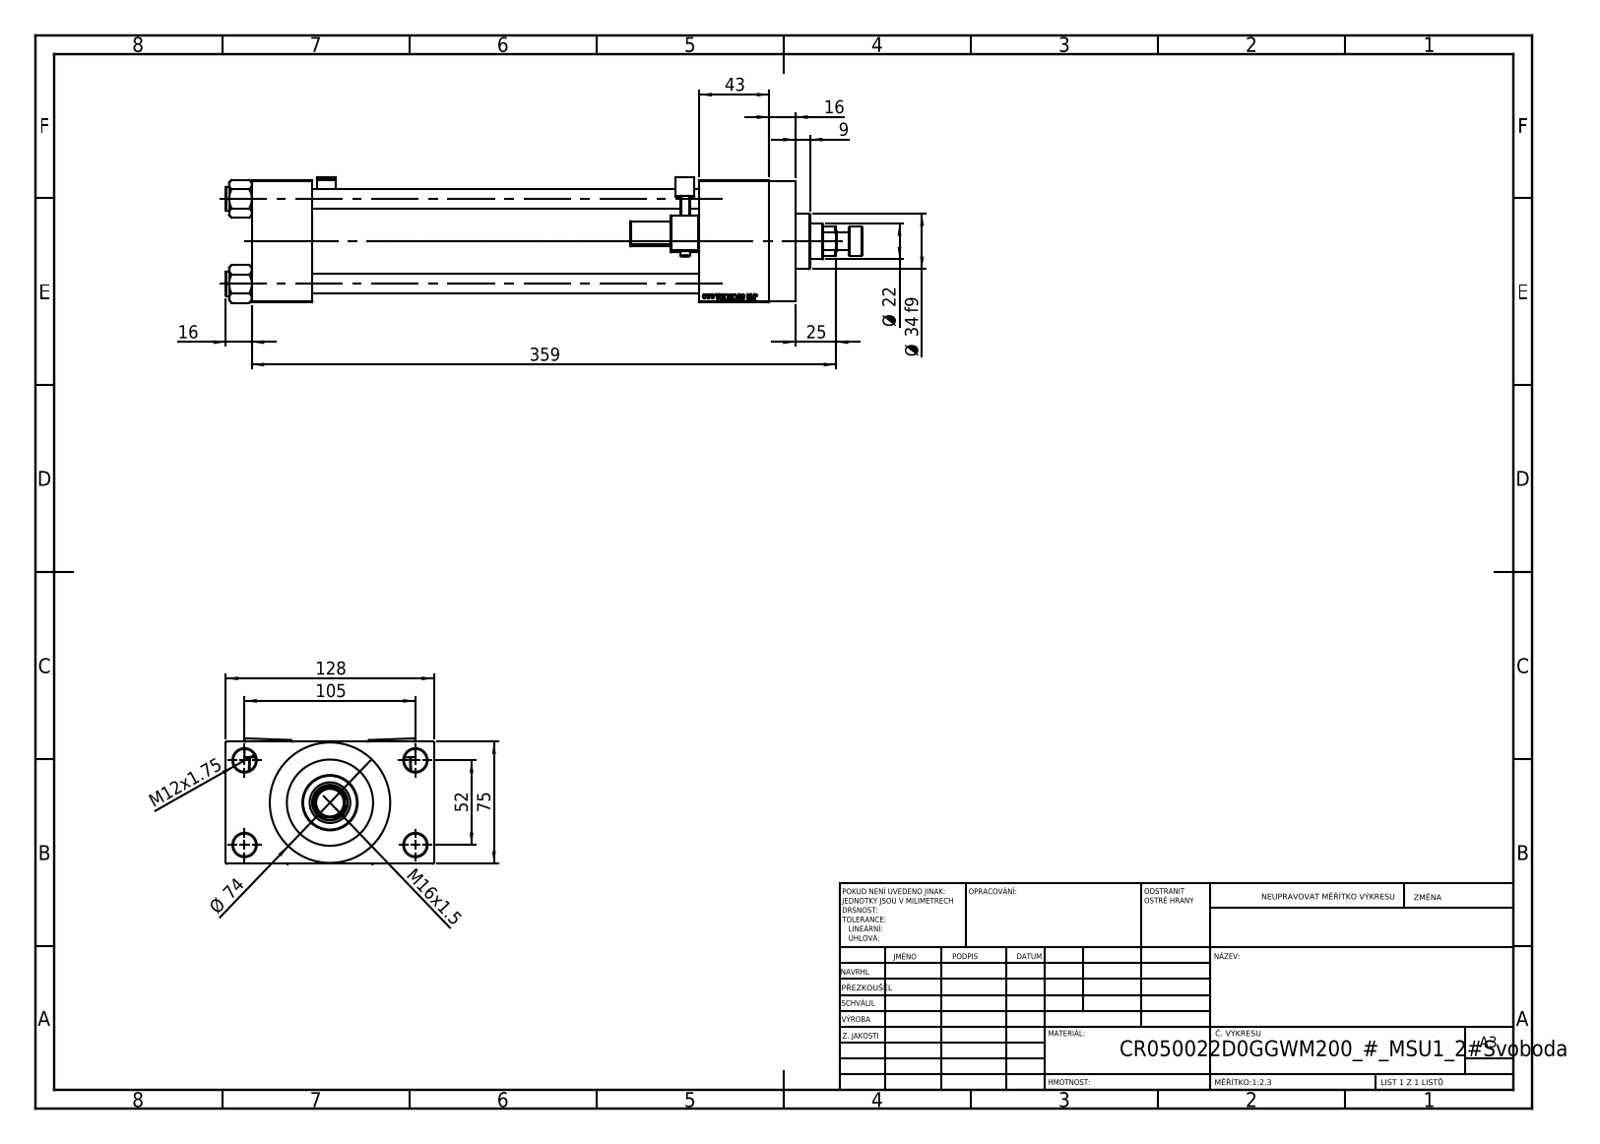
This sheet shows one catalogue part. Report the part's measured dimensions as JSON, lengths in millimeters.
{"part_name": "V215CR_ROD_END_W; V215CR_D_TYCINKA; V215CR_VCP_D; V215CR_MSU (+3 more)", "step_written_by": "SolidWorks 2019 (CONFIG_CONTROL_DESIGN)", "units": "millimeters", "bodies": {"solids": 14, "faces": 1272, "planar": 559, "cylindrical": 153, "other": 560}, "overall_size": [391, 128, 77.3], "volume_mm3": 1090000, "surface_area_mm2": 278021, "round_holes": [[12, 4], [14, 4], [7, 2], [20.96, 2], [30, 2], [10.5, 1], [22, 1], [25, 1], [41, 1], [50, 1], [53, 1]], "round_bosses_or_shafts": [[15, 4], [6, 2], [74, 1], [56, 1], [34, 1], [18, 1], [11, 1]], "partial_cylinders_radius": [[0.5, 48], [1, 2], [2.5, 2], [4, 2], [10.5, 1]], "face_to_face_distances": [75, 238, 37, 275, 101.5, 26.5, 16, 318, 281, 43], "hole_center_spacings": [26.35, 36.98, 52.3, 58.43, 58.59, 78.65, 94.37, 52]}
